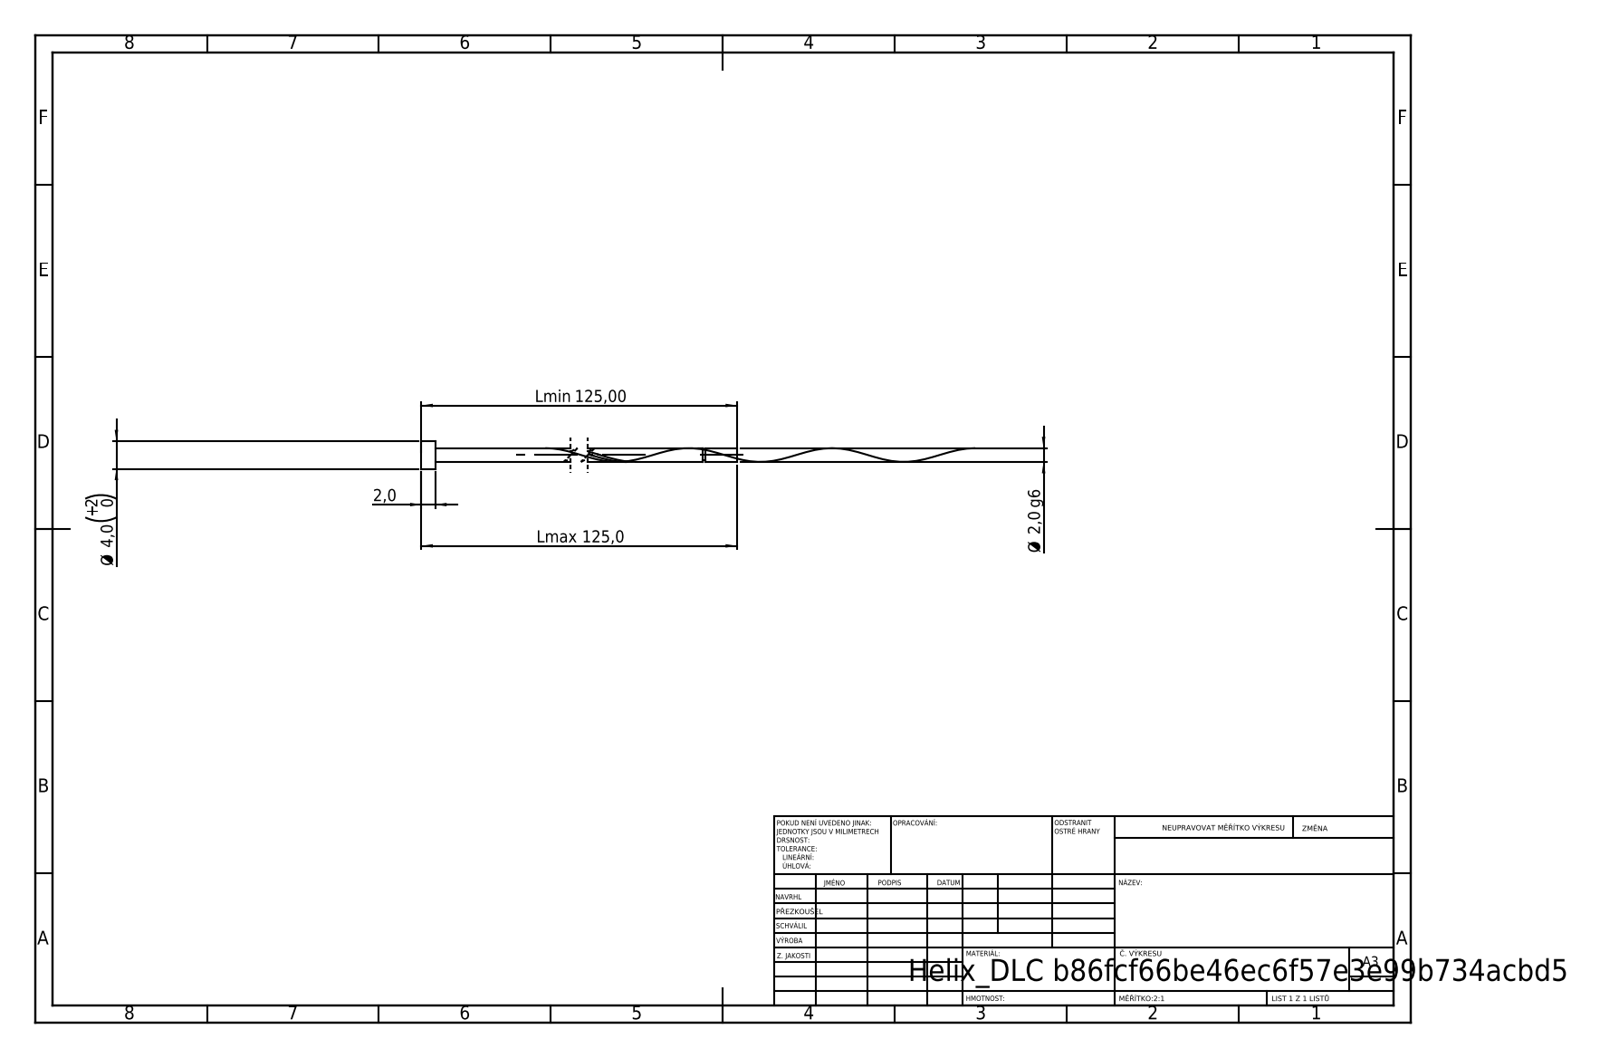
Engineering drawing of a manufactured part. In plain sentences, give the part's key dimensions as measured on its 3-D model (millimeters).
Its 3-D file was written by "SolidWorks 2019 (CONFIG_CONTROL_DESIGN)". It is 1 solid with 16 faces: 6 planar, 9 cylindrical and 1 other. Overall it measures 125 by 4 by 4 millimeters. Its volume is 495 cubic millimeters and its surface area 1 100 square millimeters. Round bosses or shafts: 1 of diameter 4, 1 of diameter 2, 1 of diameter 1.6. The main face-to-face distances are 2, 125, 123, 120.48, 118.48, 4.52, 120.08, 118.08, 0.4, 4.92.
